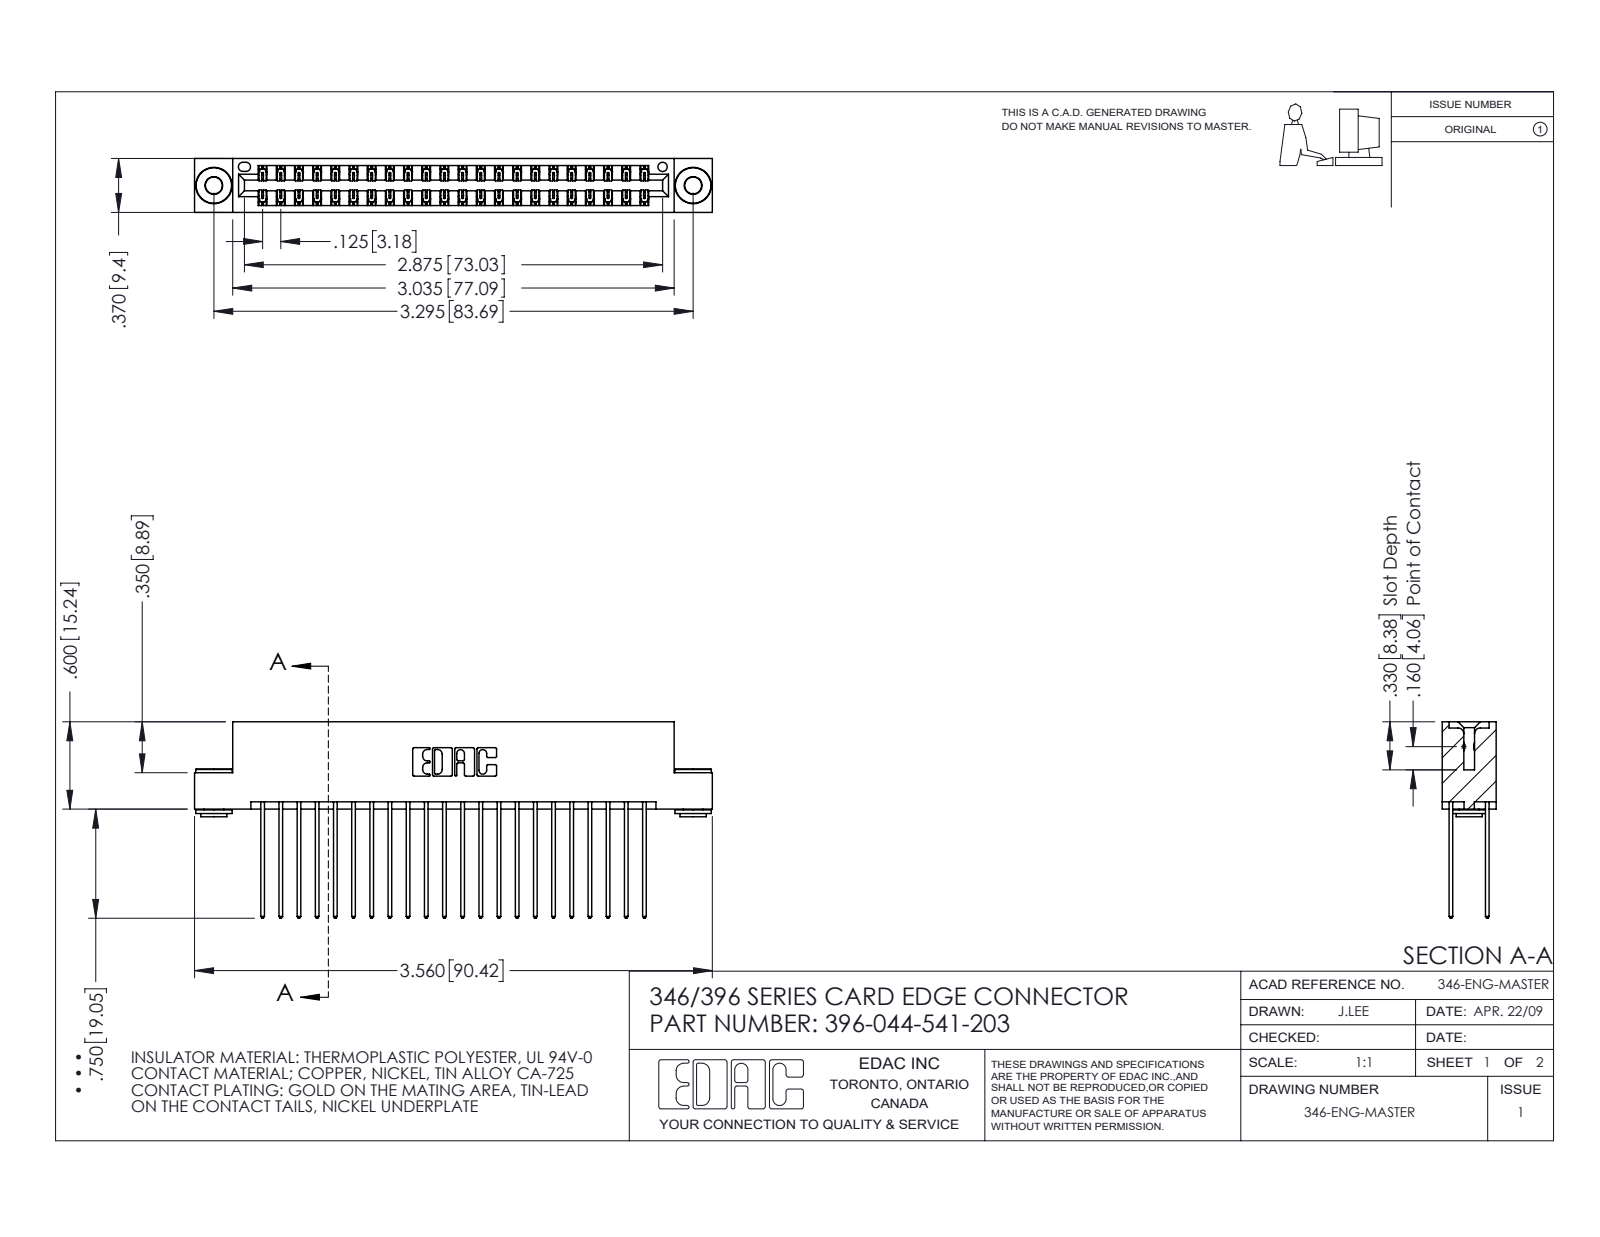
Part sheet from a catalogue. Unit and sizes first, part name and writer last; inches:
Units: inches
Overall size (bounding box): 3.56 × 1.35 × 0.37
Round holes (diameter × count): ⌀0.116 ×2, ⌀0.156 ×2, ⌀0.064 ×1
Round bosses / shafts (diameter × count): ⌀0.25 ×2, ⌀0.18 ×2, ⌀0.136 ×2
Partial cylindrical surfaces — rounded edges, fillets, slot ends (radius × count): R0.006 ×66, R0.01 ×44, R0.01 ×22, R0.007 ×6, R0.031 ×6, R0.026 ×3, R0.014 ×2, R0.022 ×2
Main face-to-face distances: 0.048, 0.322, 0.25, 0.025, 0.072, 0.298, 0.37, 0.275, 0.225, 0.148
Hole centre spacings: 0.246, 3.087, 3.295
Volume: 0.545 in³ · Surface area: 20.76 in²
Bodies: 47 solids, 2448 faces (1626 planar, 814 cylindrical, 8 other)
Part name (STEP PRODUCT): 346 Part_Flush Mounting Lugs - 0.156 Dia-TH; 345-292-001_345-293-141; 345-250-002_345-250-002-102; 396-044-541-203
STEP written by: SolidWorks 2016 (CONFIG_CONTROL_DESIGN)
